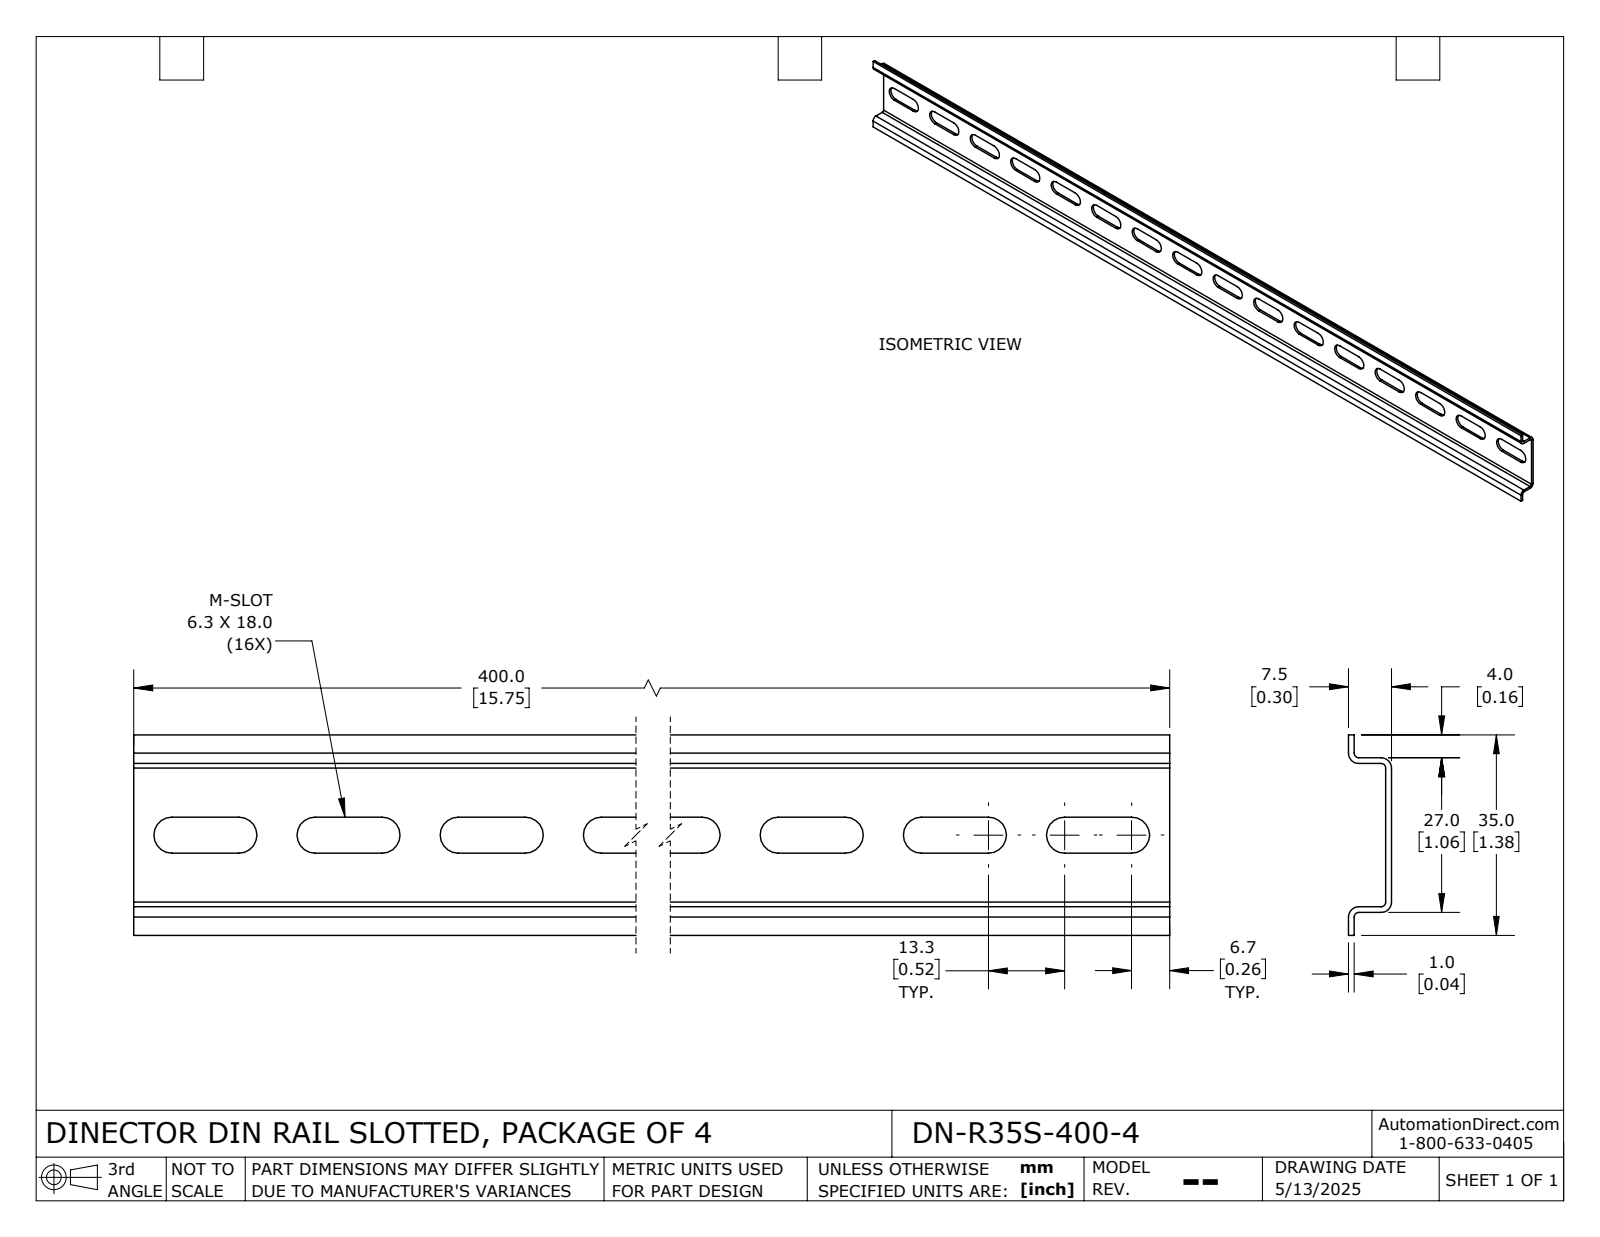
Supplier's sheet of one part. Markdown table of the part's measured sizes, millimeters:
| quantity | value |
| --- | --- |
| part name | DN-R35S-400-4_Default |
| STEP written by | SolidWorks 2024 (CONFIG_CONTROL_DESIGN) |
| units | millimeters |
| bodies | 1 solid, 86 faces (46 planar, 40 cylindrical, 0 other) |
| overall size | 400 × 35 × 7.5 |
| volume | 16 629 mm³ |
| surface area | 34 841 mm² |
| partial cylindrical surfaces (radius × count) | 3.15 × 32, 0.8 × 4, 1.8 × 4 |
| main face-to-face distances | 1, 6.5, 26, 7.5, 5.5, 27, 25, 4, 5, 30 |
